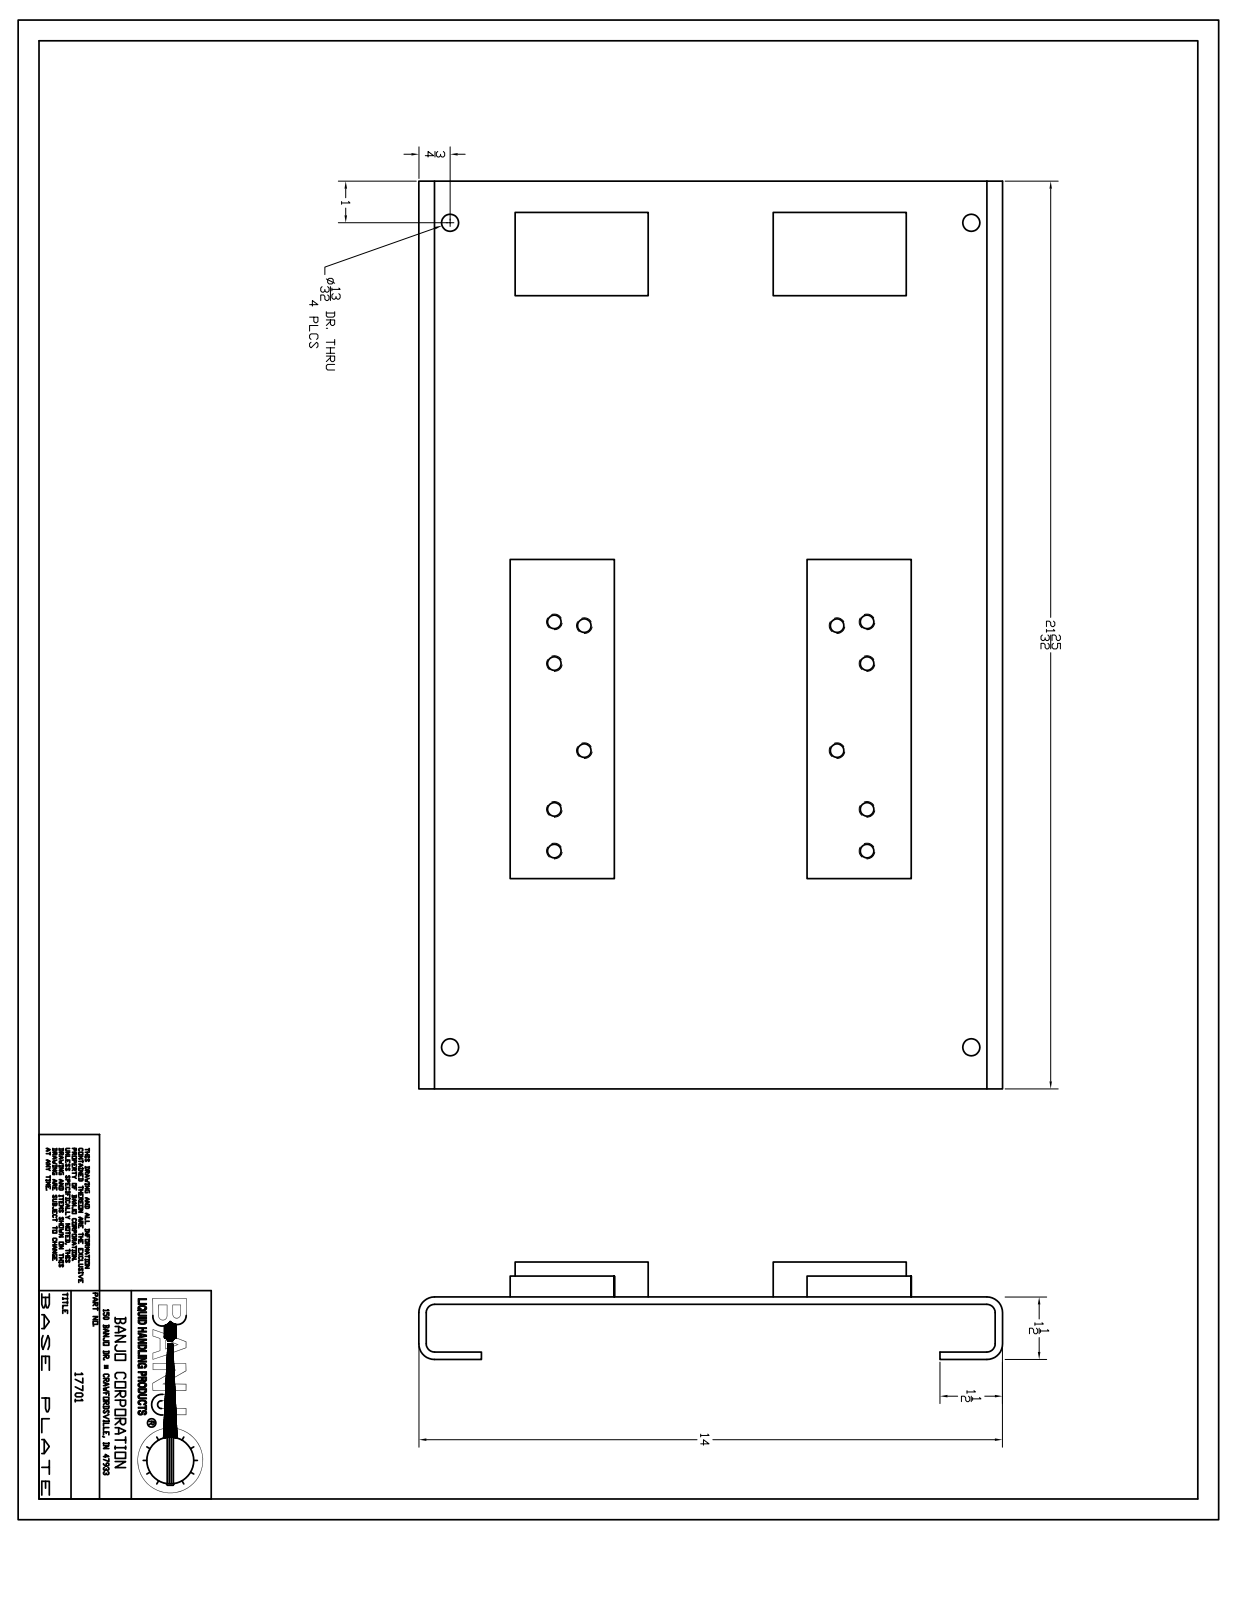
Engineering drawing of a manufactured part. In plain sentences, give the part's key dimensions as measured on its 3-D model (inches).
The part is named "17701". Its 3-D file was written by "Autodesk Inventor 2015 (AUTOMOTIVE_DESIGN)". It is 1 solid with 122 faces: 34 planar, 60 cylindrical and 28 other. Overall it measures 21.79 by 14 by 2.33 inches. Its volume is 102.2 cubic inches and its surface area 876 square inches. Round holes: 12 of diameter 0.307, 4 of diameter 0.41. Partial cylindrical surfaces (rounded edges, fillets, slot ends): 16 of radius 0.125, 12 of radius 0.03, 4 of radius 0.18, 4 of radius 0.375. The main face-to-face distances are 0.179, 1.321, 1.5, 1.142, 2, 1.821, 0.679, 0.5, 13.821, 13.642. The hole center spacings are 1, 4.5, 7.5, 7.567, 8.746, 0.724, 1.16, 1.583.
